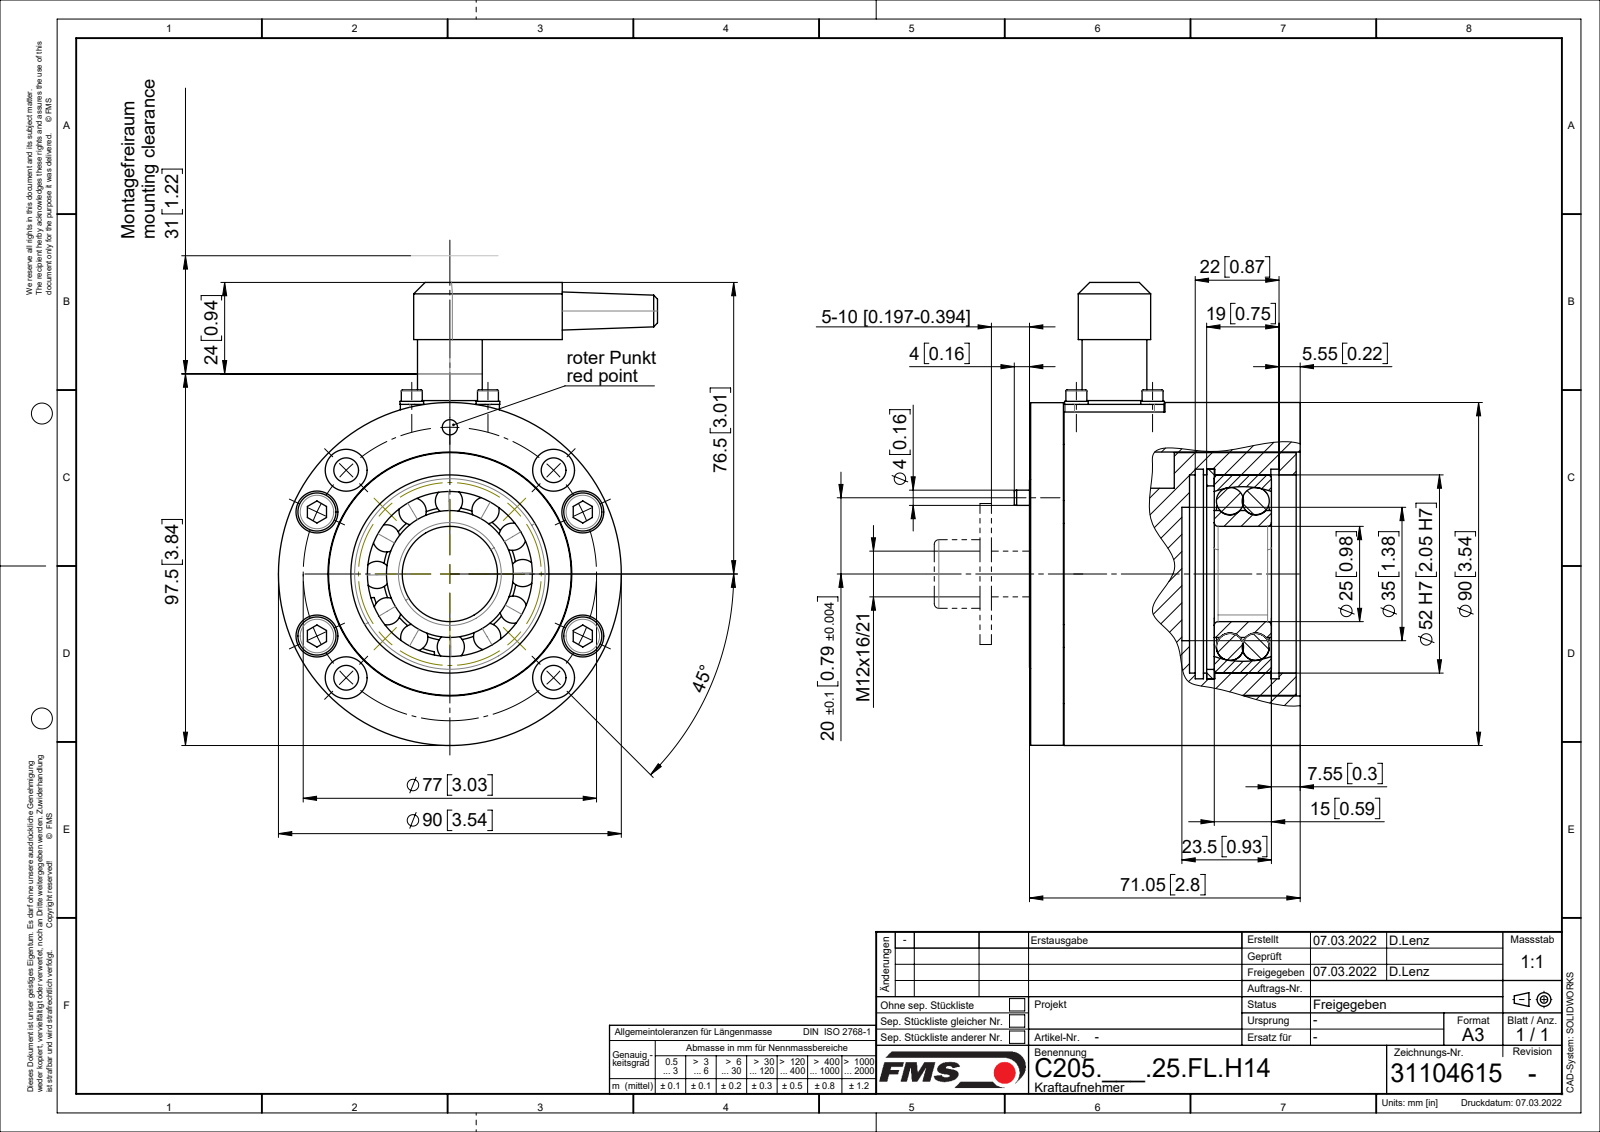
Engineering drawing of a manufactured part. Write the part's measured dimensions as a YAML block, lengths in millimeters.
part_name: "Zyl-Schr DIN912_M3x6; Zyl-Schr DIN912_M6x30; 31104488_01; 31104484_Stp_01 (+8 more)"
step_written_by: "SolidWorks 2018 (CONFIG_CONTROL_DESIGN)"
units: millimeters
bodies: {solids: 47, faces: 617, planar: 193, cylindrical: 263, other: 161}
overall_size: [121.5, 99.5, 96.05]
volume: 321443
surface_area: 127430
round_holes:
  - {diameter: 6.5, count: 8}
  - {diameter: 11, count: 8}
  - {diameter: 2.5, count: 6}
  - {diameter: 2, count: 5}
  - {diameter: 3.1, count: 4}
  - {diameter: 3.2, count: 4}
  - {diameter: 5, count: 4}
  - {diameter: 7, count: 4}
  - {diameter: 4, count: 2}
  - {diameter: 3, count: 1}
  - {diameter: 10.2, count: 1}
  - {diameter: 12, count: 1}
round_bosses_or_shafts:
  - {diameter: 1.5, count: 5}
  - {diameter: 10, count: 4}
  - {diameter: 6.2, count: 4}
  - {diameter: 6, count: 4}
  - {diameter: 5.5, count: 4}
  - {diameter: 3, count: 4}
  - {diameter: 90, count: 1}
  - {diameter: 89.9, count: 1}
partial_cylinders:
  - {radius: 0.1, count: 4}
  - {radius: 2.5, count: 4}
  - {radius: 0.5, count: 2}
  - {radius: 4.24, count: 2}
  - {radius: 5, count: 2}
  - {radius: 9.5, count: 1}
  - {radius: 20.8, count: 1}
  - {radius: 24.1, count: 1}
face_to_face_distances: [6, 6.5, 32, 2, 25.5, 33.05, 38, 8.6, 29.1, 37.7]
hole_center_spacings: [20, 38.5, 13.37, 14.14, 38.49, 44.16, 54.44, 63.07]
